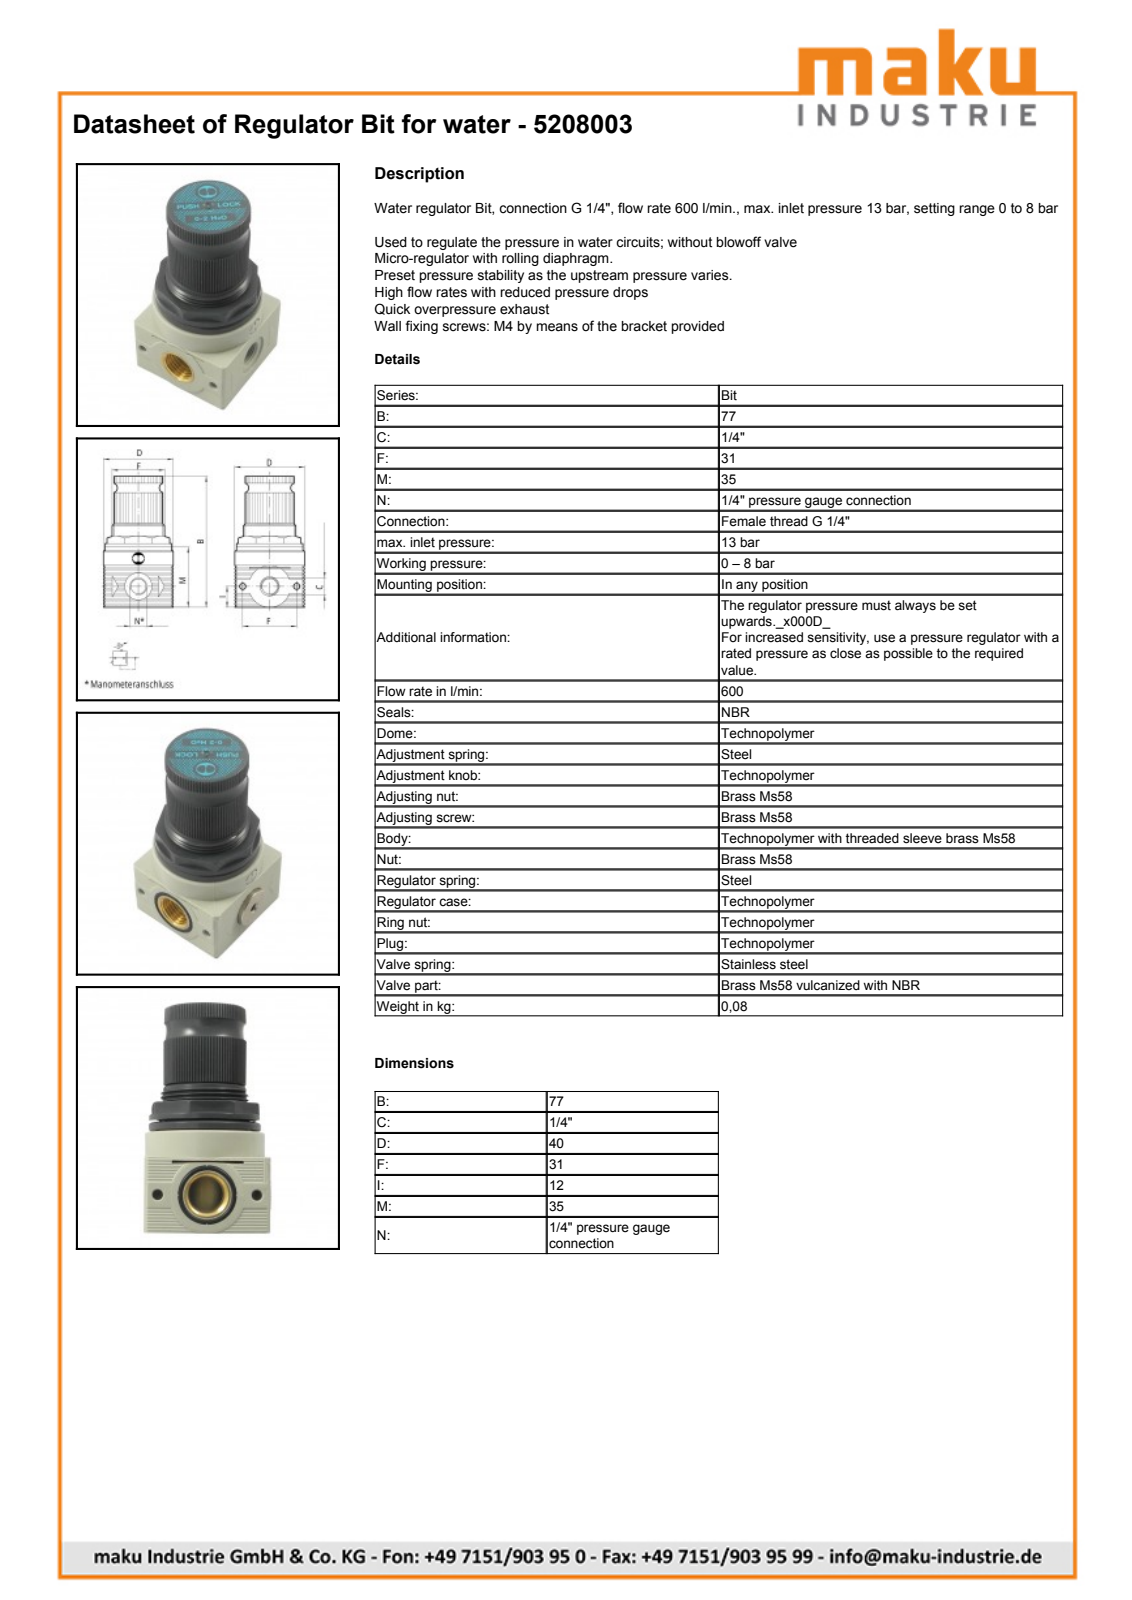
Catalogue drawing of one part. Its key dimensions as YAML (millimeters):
part_name: "5208003; 5208003-BD; 5208003-KN; 1/8-BIT"
step_written_by: "PARTsolutions (AUTOMOTIVE_DESIGN)"
units: millimeters
bodies: {solids: 3, faces: 127, planar: 92, cylindrical: 27, other: 8}
overall_size: [77, 41.5, 40]
volume: 76444
surface_area: 18319
round_holes:
  - {diameter: 4, count: 2}
  - {diameter: 8.57, count: 1}
  - {diameter: 11.45, count: 1}
  - {diameter: 15.5, count: 1}
round_bosses_or_shafts:
  - {diameter: 39.9, count: 1}
  - {diameter: 38, count: 1}
  - {diameter: 37.6, count: 1}
  - {diameter: 30, count: 1}
  - {diameter: 28, count: 1}
  - {diameter: 24, count: 1}
  - {diameter: 15, count: 1}
  - {diameter: 9.73, count: 1}
partial_cylinders:
  - {radius: 12, count: 1}
face_to_face_distances: [32, 40, 1, 9, 10, 39.95, 77, 45, 39, 19]
hole_center_spacings: [15.5, 31]
